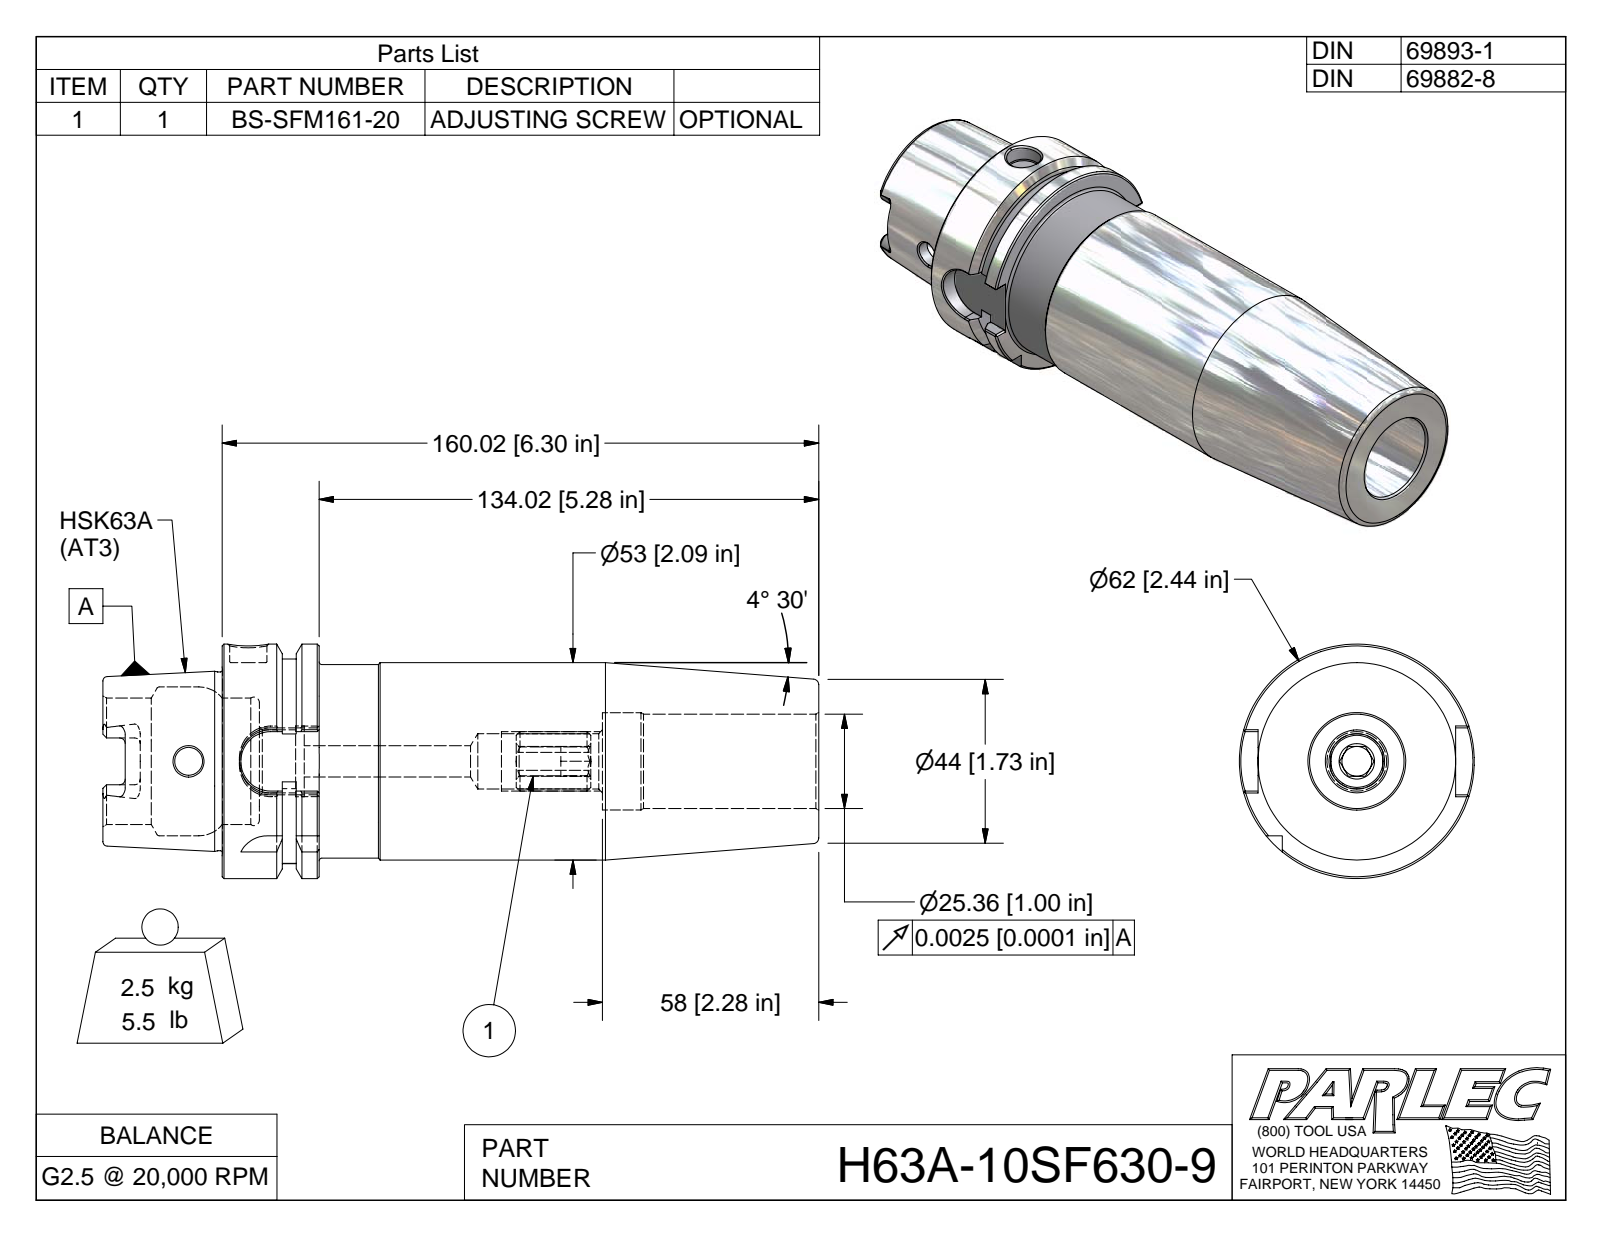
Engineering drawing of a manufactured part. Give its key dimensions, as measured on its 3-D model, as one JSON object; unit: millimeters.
{"part_name": "H63A-10SF630-9; H63A-10SF630-9-1; BS-SFM161-20", "step_written_by": "Autodesk Inventor 2009 (AUTOMOTIVE_DESIGN)", "units": "millimeters", "bodies": {"solids": 2, "faces": 167, "planar": 65, "cylindrical": 37, "other": 65}, "overall_size": [192, 63, 63], "volume_mm3": 319900, "surface_area_mm2": 52320, "round_holes": [[7.5, 1], [10, 1], [16.9, 1], [19, 1], [25.4, 1], [26.1, 1], [34, 1], [40, 1]], "round_bosses_or_shafts": [[63, 1], [53, 1], [52, 1], [48, 1]], "partial_cylinders_radius": [[1.5, 6], [8, 5], [2.9, 4], [27.5, 1]], "face_to_face_distances": [134, 160, 26, 58, 6.1, 9.9, 10, 16, 150, 32]}
